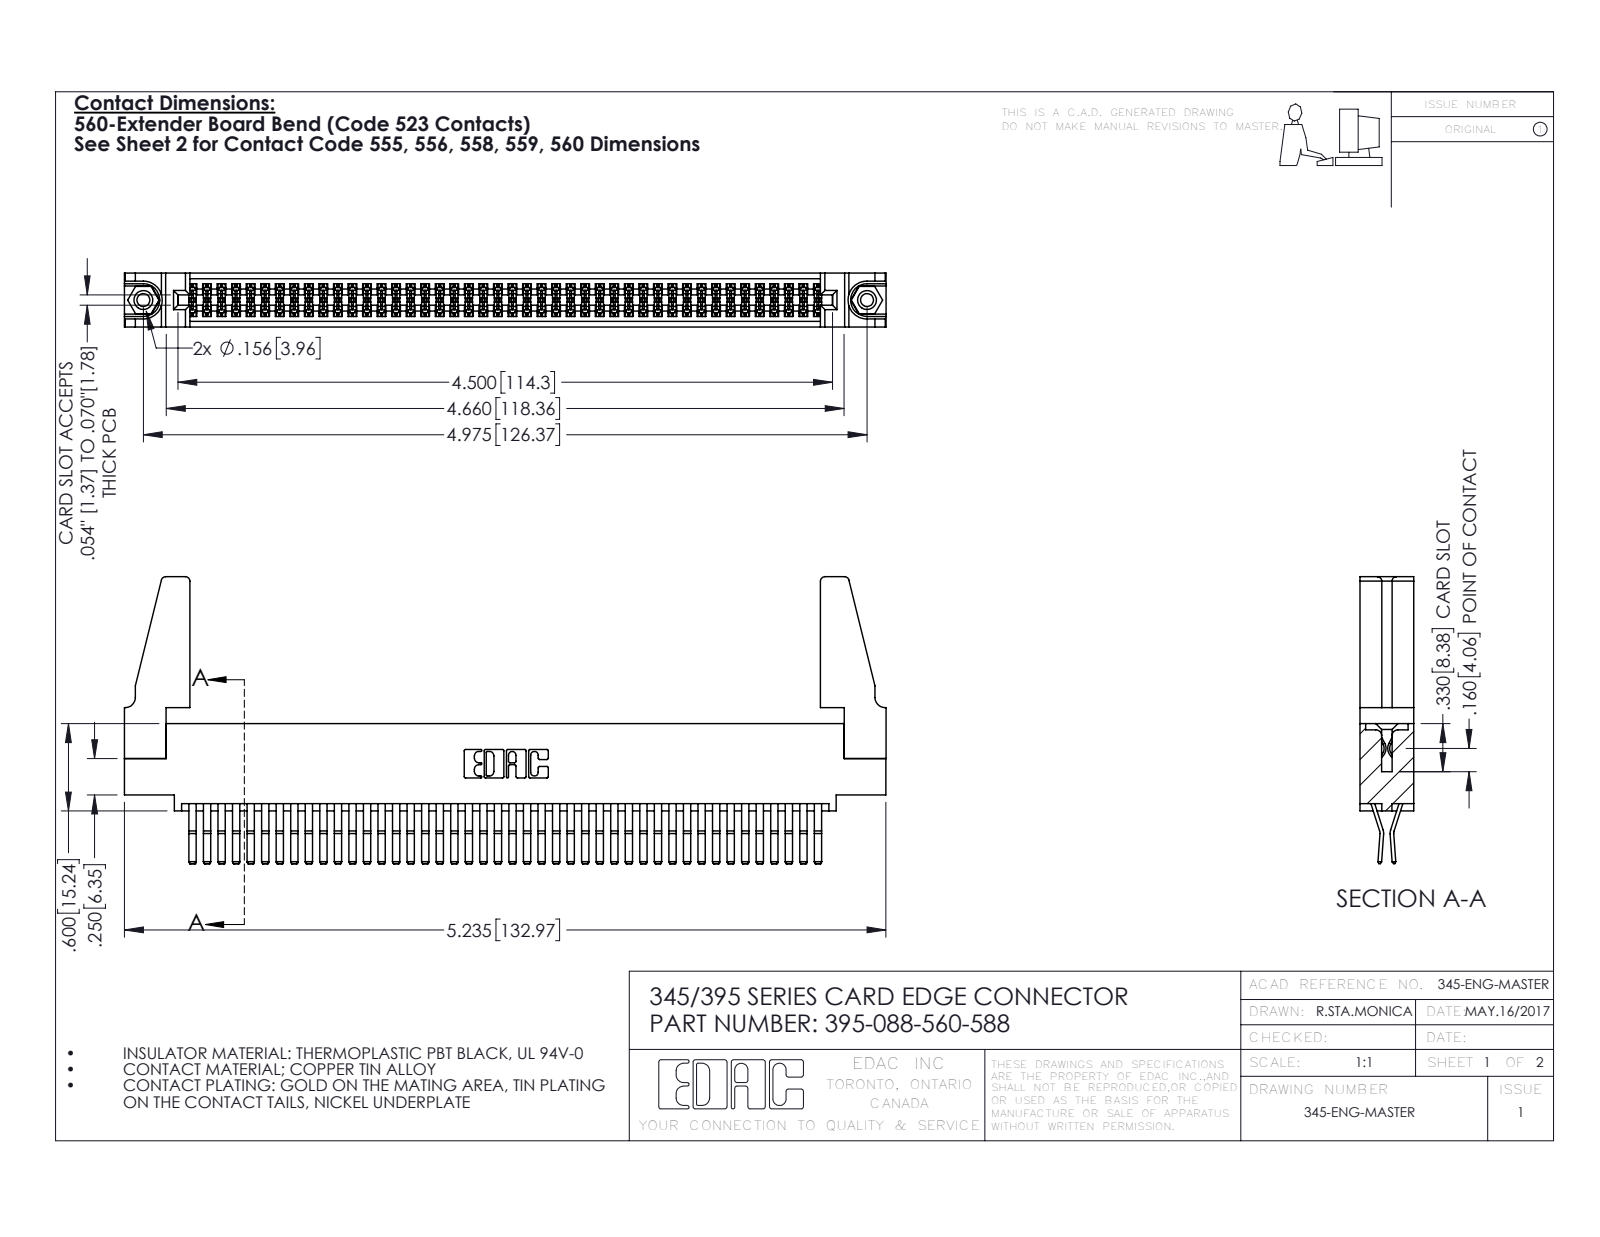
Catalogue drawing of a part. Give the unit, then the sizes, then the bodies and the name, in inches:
Units: inches
Overall size (bounding box): 5.236 × 1.972 × 0.37
Round holes (diameter × count): ⌀0.089 ×2, ⌀0.125 ×2, ⌀0.156 ×2, ⌀0.064 ×1
Round bosses / shafts (diameter × count): ⌀0.155 ×2
Partial cylindrical surfaces — rounded edges, fillets, slot ends (radius × count): R0.006 ×132, R0.01 ×22, R0.03 ×8, R0.007 ×6, R0.031 ×6, R0.026 ×3, R0.01 ×2, R0.014 ×2
Main face-to-face distances: 0.072, 0.298, 0.025, 0.37, 0.2, 0.098, 0.272, 0.225, 0.175, 0.149
Hole centre spacings: 0.27, 4.739, 4.975
Volume: 1.019 in³ · Surface area: 38.14 in²
Bodies: 93 solids, 4830 faces (3060 planar, 1754 cylindrical, 16 other)
Part name (STEP PRODUCT): 345-250-001_345-250-001-102; 345-220-078_345-220-088; 345 Part_0.110 Offset - 0.156 Dia-TH; 395-088-560-588 (+1 more)
STEP written by: SolidWorks 2016 (CONFIG_CONTROL_DESIGN)
